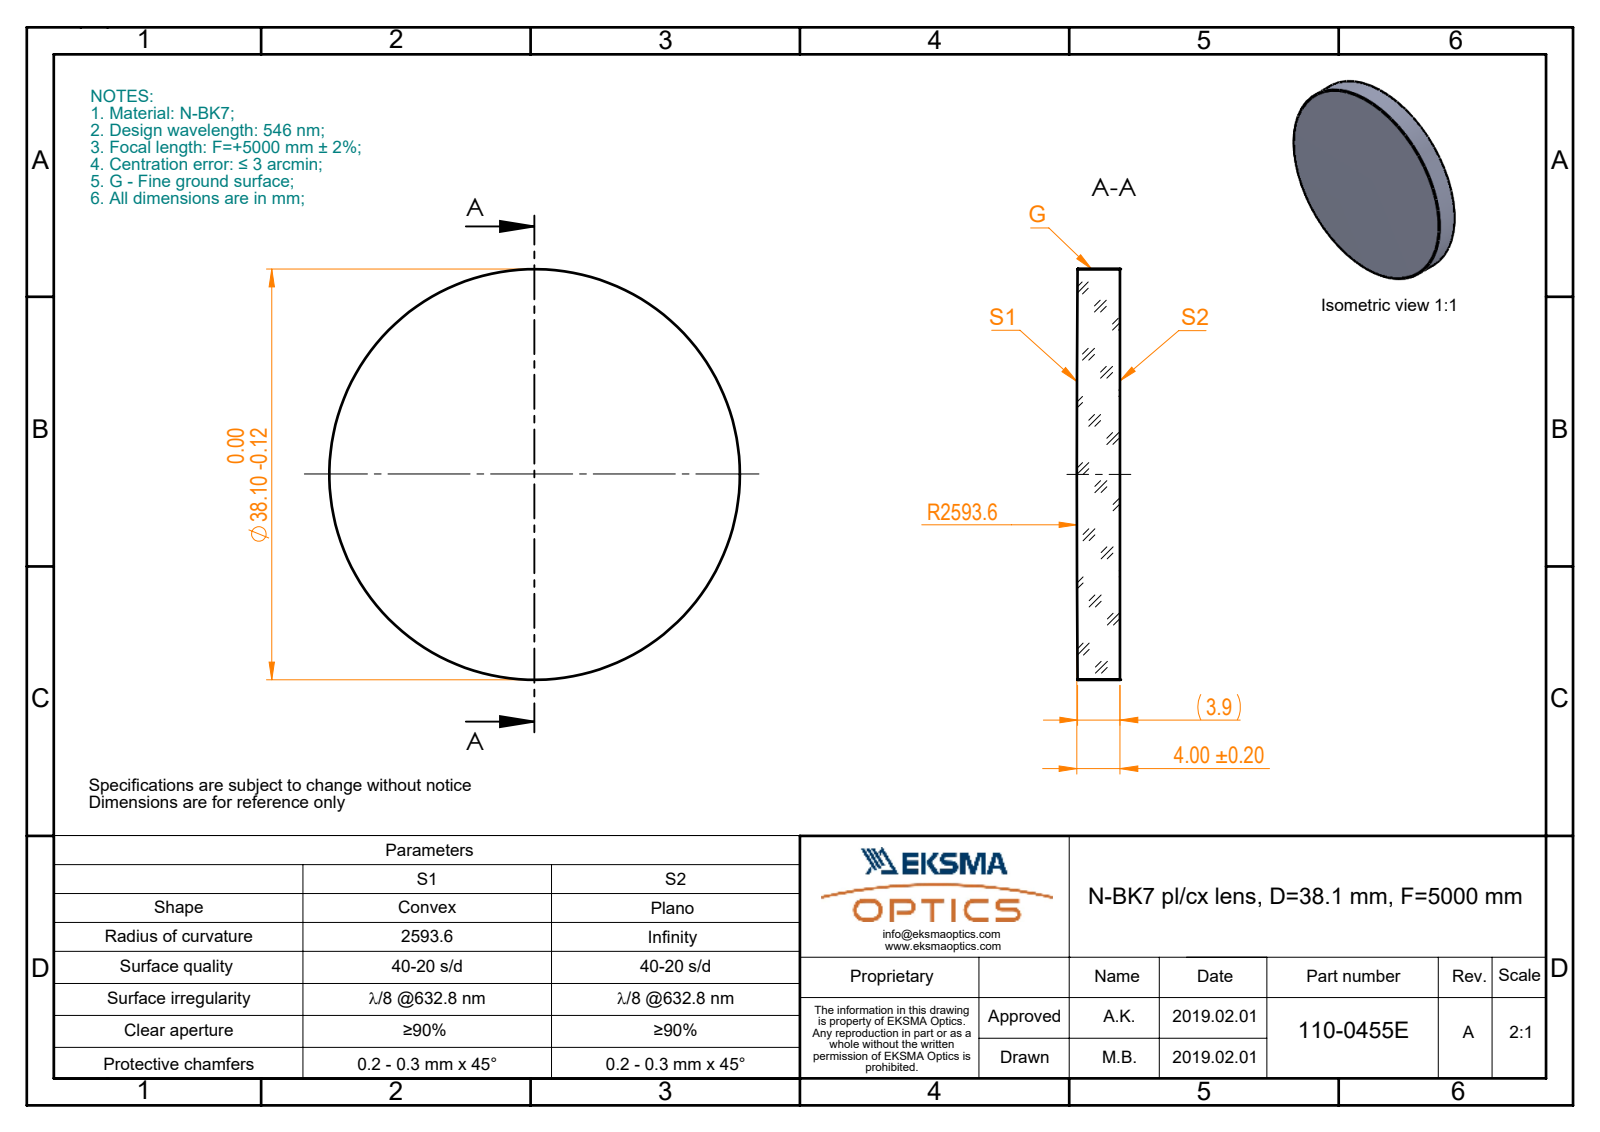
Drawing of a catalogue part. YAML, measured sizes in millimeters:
part_name: "110-0455E BK7 pl-cx 38.1 F5000"
step_written_by: "SolidWorks 2017 (CONFIG_CONTROL_DESIGN)"
units: millimeters
bodies: {solids: 1, faces: 5, planar: 1, cylindrical: 2, other: 2}
overall_size: [38.1, 38.1, 4]
volume: 4520
surface_area: 2751
round_bosses_or_shafts:
  - {diameter: 38.1, count: 1}
